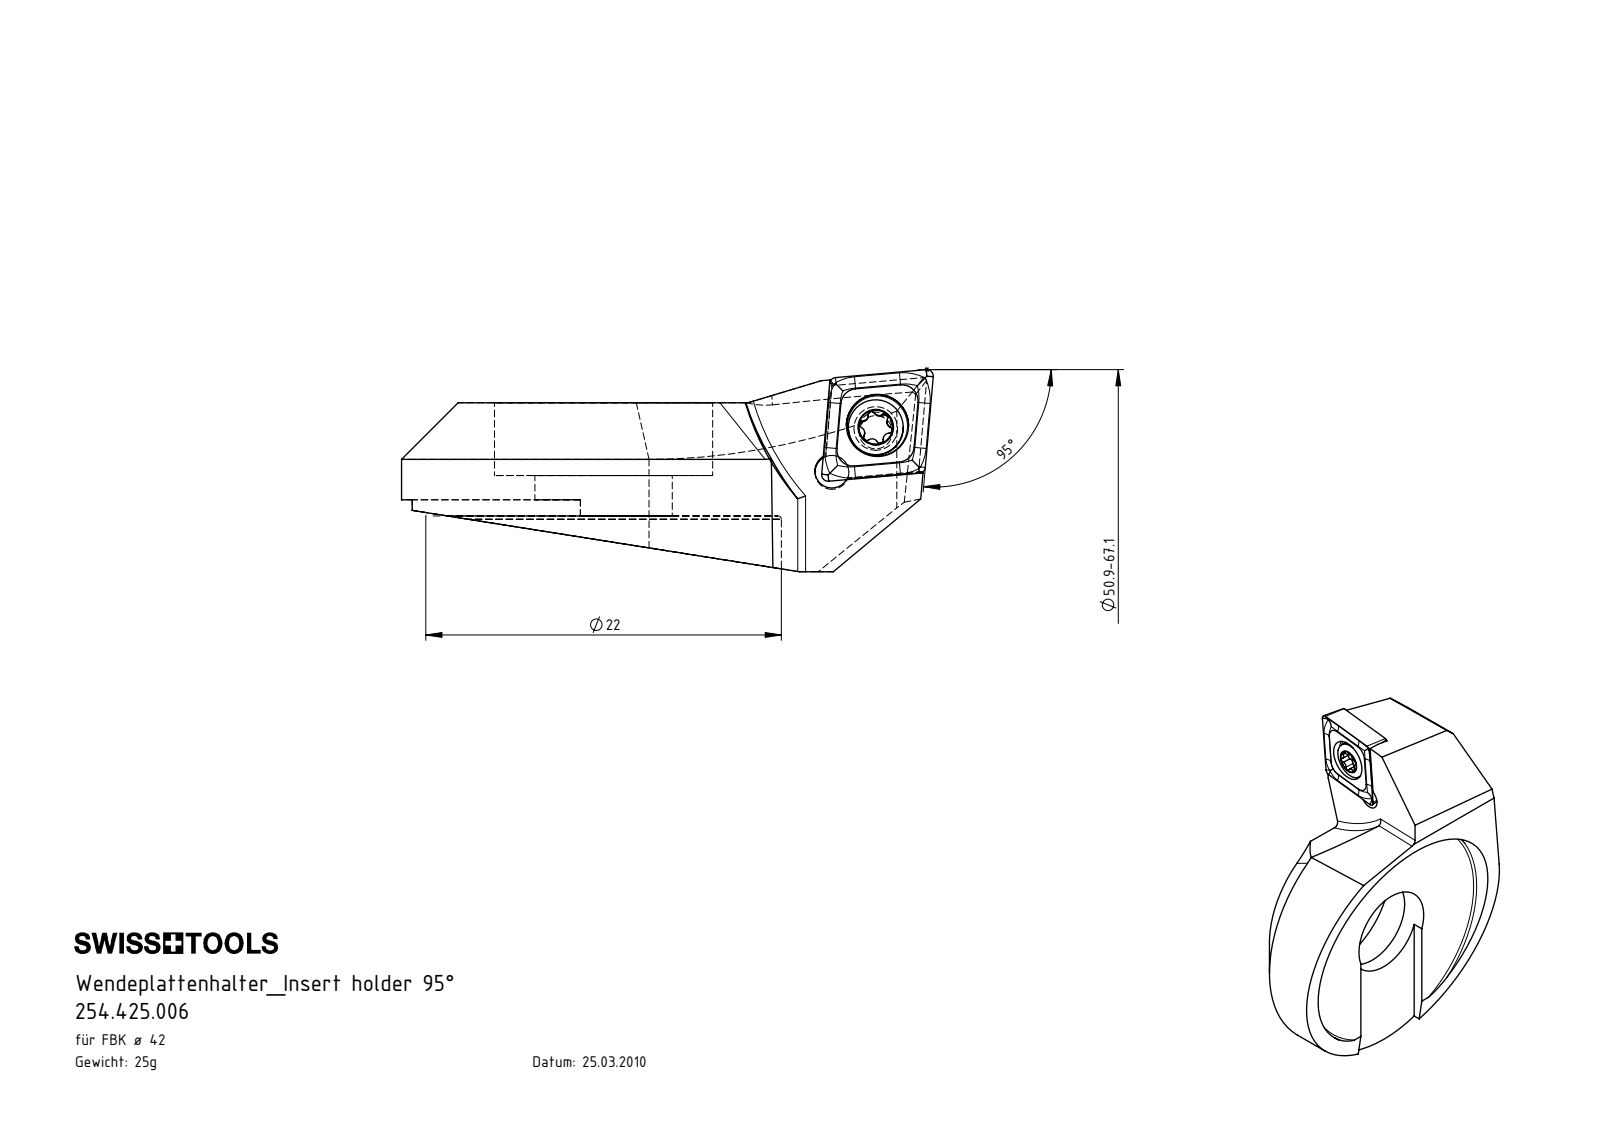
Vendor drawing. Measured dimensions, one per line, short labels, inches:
name: WCA-ER2.001.006_A; 254.425.006; F42-WCA.002.009_C_fertigbearbeitet; CCMT060204
written by: SolidWorks 2017 (CONFIG_CONTROL_DESIGN)
unit: in
bodies: 5 solids, 147 faces (48 planar, 45 cylindrical, 54 other)
size: 1.295 × 0.984 × 0.492
volume: 0.197 in³; area: 4.222 in²
holes: 1× ⌀0.081, 1× ⌀0.083, 1× ⌀0.11, 1× ⌀0.152, 1× ⌀0.335, 1× ⌀0.531
bosses: 1× ⌀0.134, 1× ⌀0.098
rounds: 6× R0.008, 5× R0.014, 2× R0.02, 1× R0.014, 1× R0.041, 1× R0.197, 1× R0.433, 1× R0.492
face distances: 0.276, 0.264, 0.177, 0.165, 0.098, 0.09, 0.236, 0.224, 0.059, 0.039
hole spacings: 0.151, 0.157
